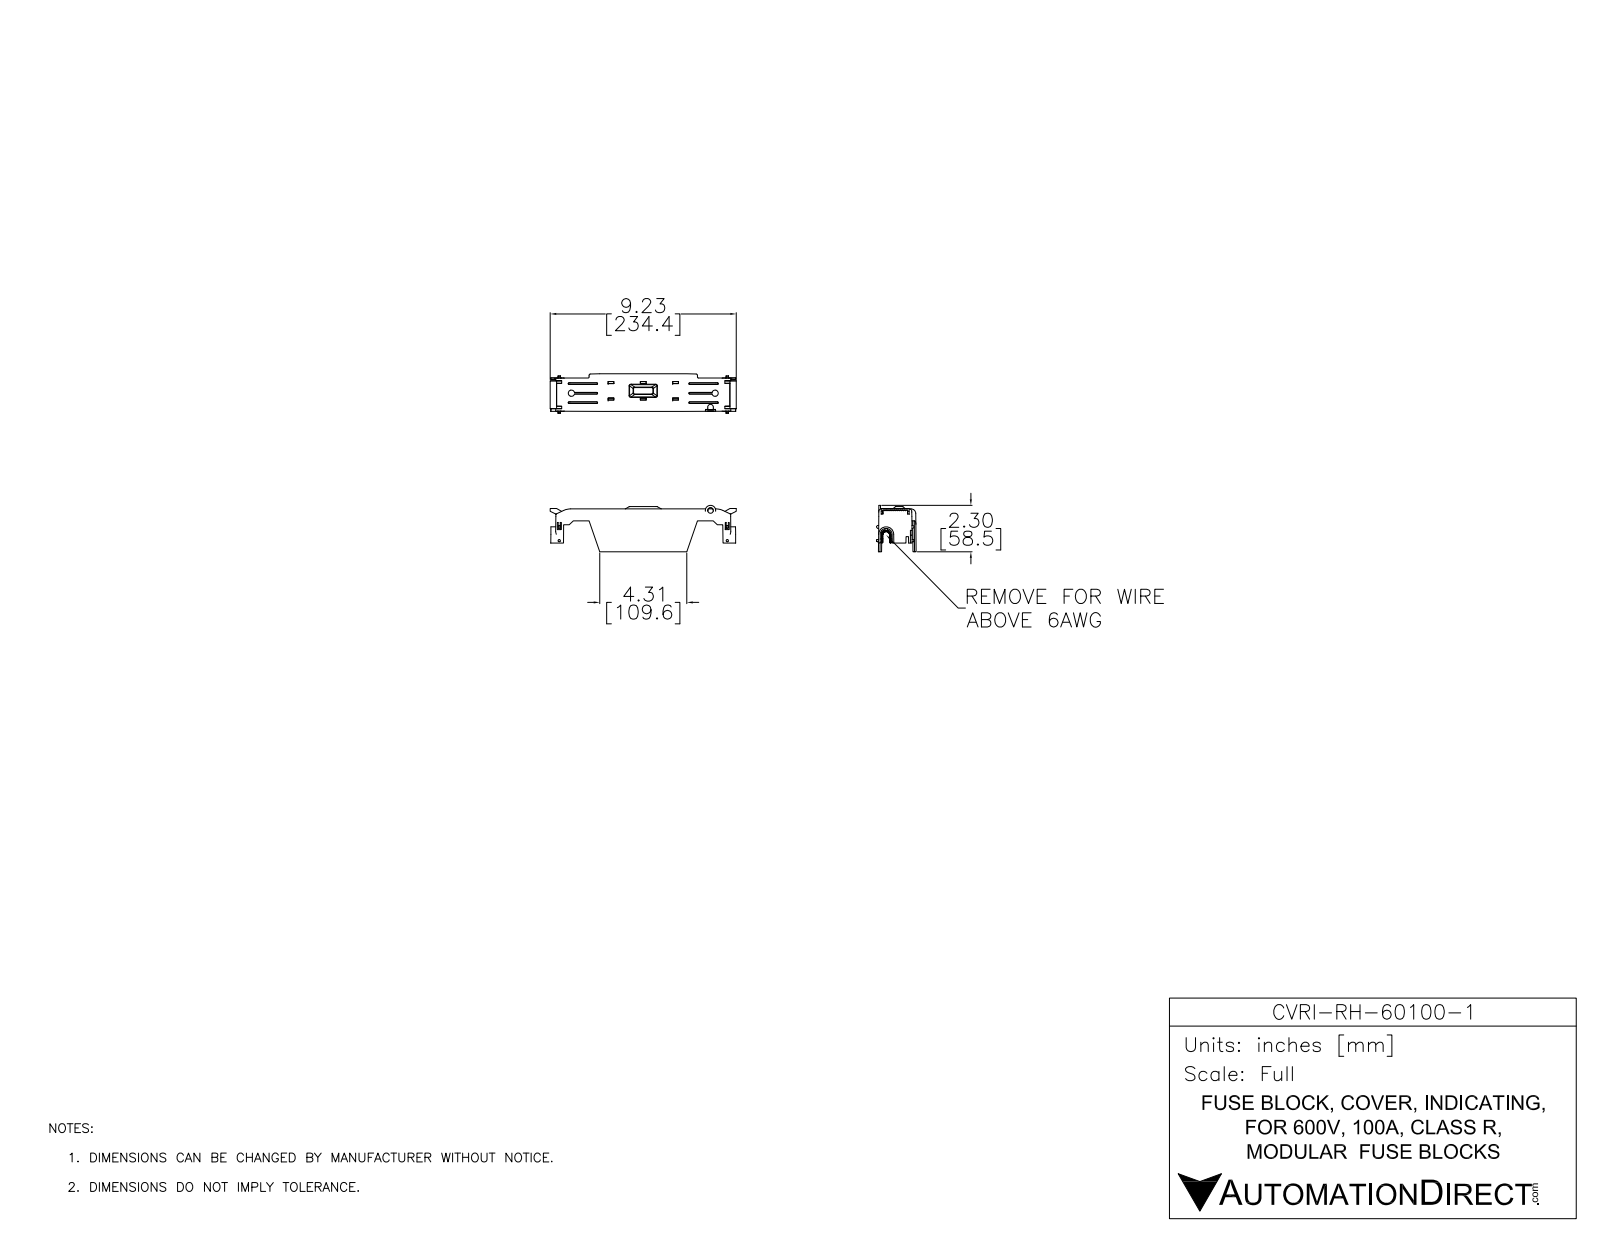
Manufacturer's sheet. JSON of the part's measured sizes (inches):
{"part_name": "CVRI-RH-60100-1", "step_written_by": "SolidWorks 2017 (AUTOMOTIVE_DESIGN)", "units": "inches", "bodies": {"solids": 1, "faces": 1436, "planar": 948, "cylindrical": 102, "other": 386}, "overall_size": [9.23, 2.304, 1.964], "volume_in3": 4.09, "surface_area_in2": 110.1, "round_holes": [[0.276, 1]], "partial_cylinders_radius": [[0.039, 18], [0.118, 14], [0.031, 6], [0.059, 4], [0.01, 2], [0.02, 2], [0.167, 2], [0.63, 2]], "face_to_face_distances": [0.079, 0.197, 0.118, 0.276, 0.157, 0.803, 0.989, 1.068, 1.186, 1.265]}
